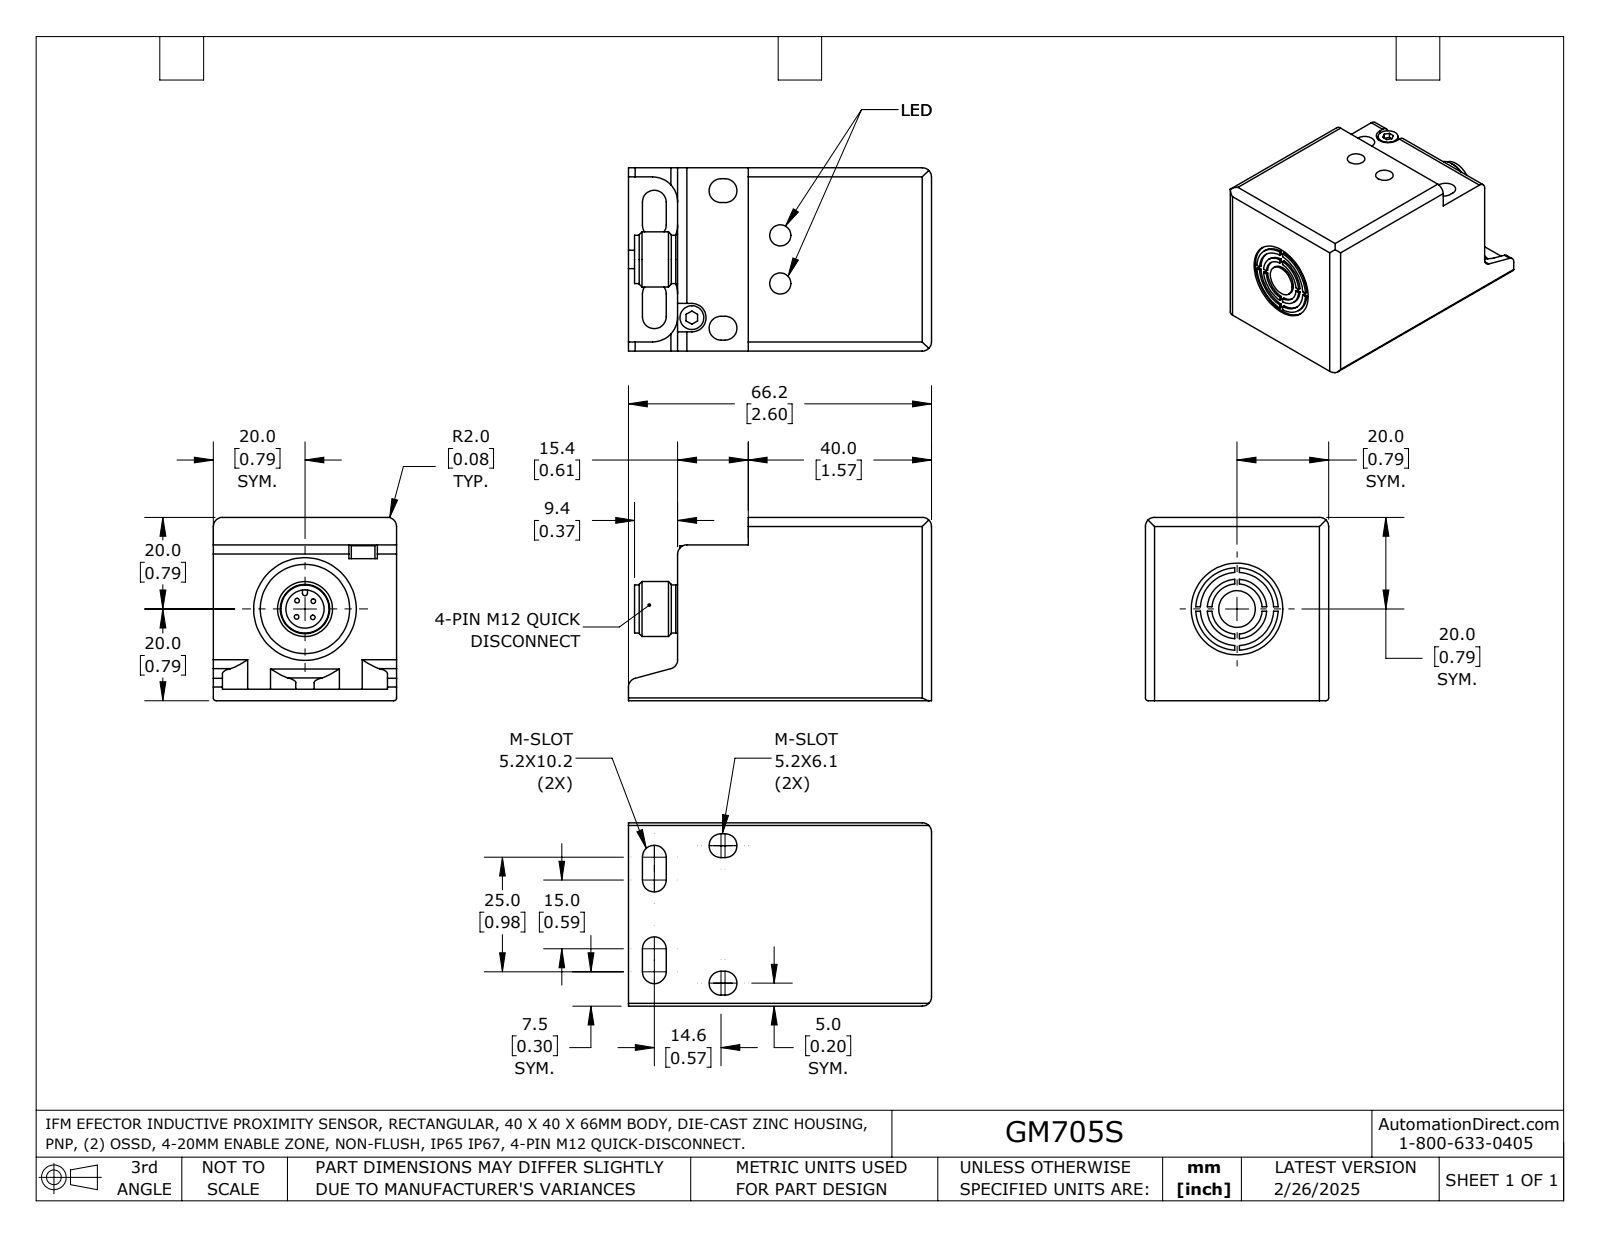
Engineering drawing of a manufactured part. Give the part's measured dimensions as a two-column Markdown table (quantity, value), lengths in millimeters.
| quantity | value |
| --- | --- |
| part name | GM705S |
| STEP written by | SolidWorks 2024 (AUTOMOTIVE_DESIGN) |
| units | millimeters |
| bodies | 1 solid, 132 faces (74 planar, 55 cylindrical, 3 other) |
| overall size | 66.15 × 40 × 40 |
| volume | 84 277 mm³ |
| surface area | 14 729 mm² |
| round holes (diameter × count) | 4.6 × 2, 8.35 × 1, 11 × 1, 16 × 1, 19.5 × 1, 20 × 1, 22.4 × 1 |
| round bosses / shafts (diameter × count) | 18 × 1, 13 × 1, 12 × 1, 10.5 × 1, 8 × 1, 5.2 × 1 |
| partial cylindrical surfaces (radius × count) | 2 × 9, 2.6 × 8, 5.5 × 4, 0.6 × 2, 0.55 × 1, 3.1 × 1 |
| main face-to-face distances | 40, 55.4, 34, 6, 2.5, 15.4, 0.5, 31.5, 37.5, 15.2 |
| hole center spacings | 10.5 |
